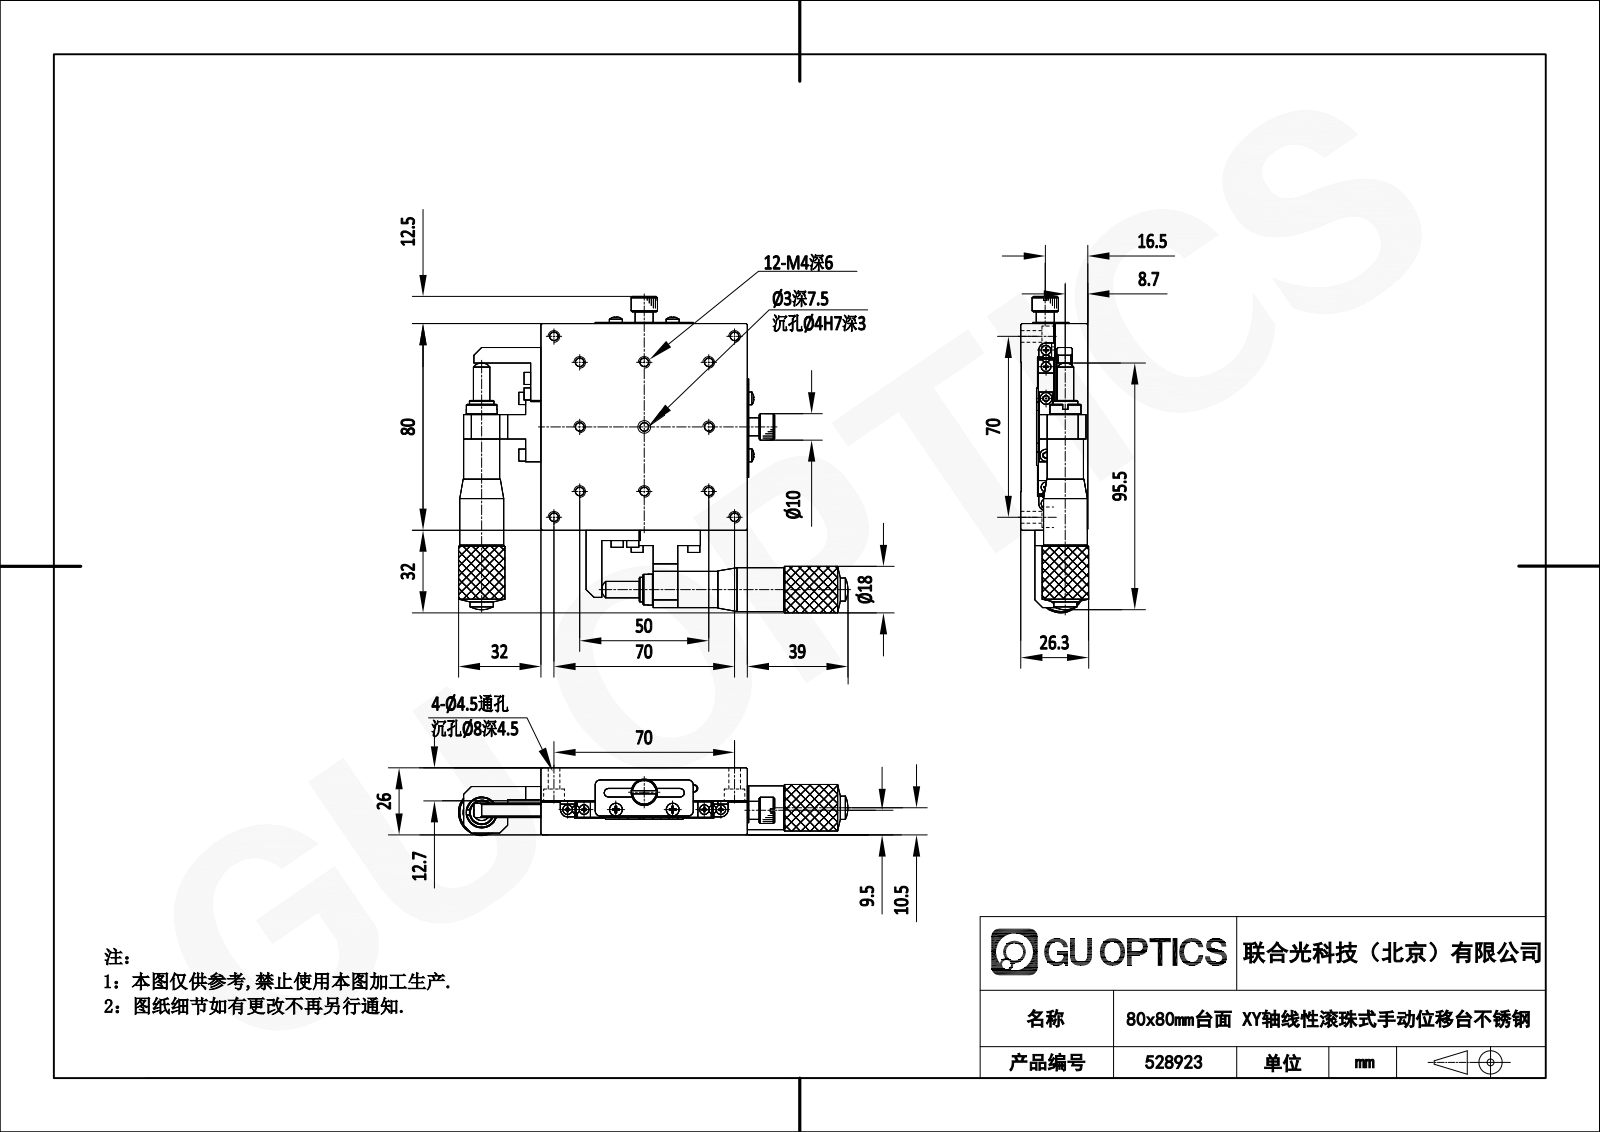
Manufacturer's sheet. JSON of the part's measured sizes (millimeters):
{"part_name": "528923", "step_written_by": "SolidWorks 2020 (CONFIG_CONTROL_DESIGN)", "units": "millimeters", "bodies": {"solids": 0, "faces": 4601, "planar": 480, "cylindrical": 1076, "other": 3045}, "overall_size": [141.88, 123.77, 30.63], "round_holes": [[2.8, 2], [3, 2], [7, 1]], "round_bosses_or_shafts": [[2.05, 26], [3.24, 12], [1.6, 8], [4, 6], [2.8, 6], [7, 5], [4.5, 4], [8, 3]], "partial_cylinders_radius": [[1.75, 16], [2, 4], [3, 4], [1.65, 2], [5, 2]], "face_to_face_distances": [6.5, 13, 0.5, 6.25, 12.5, 19.5, 6, 7, 19, 5.75], "hole_center_spacings": [6, 8.22, 12.75, 12.8, 16, 22]}
